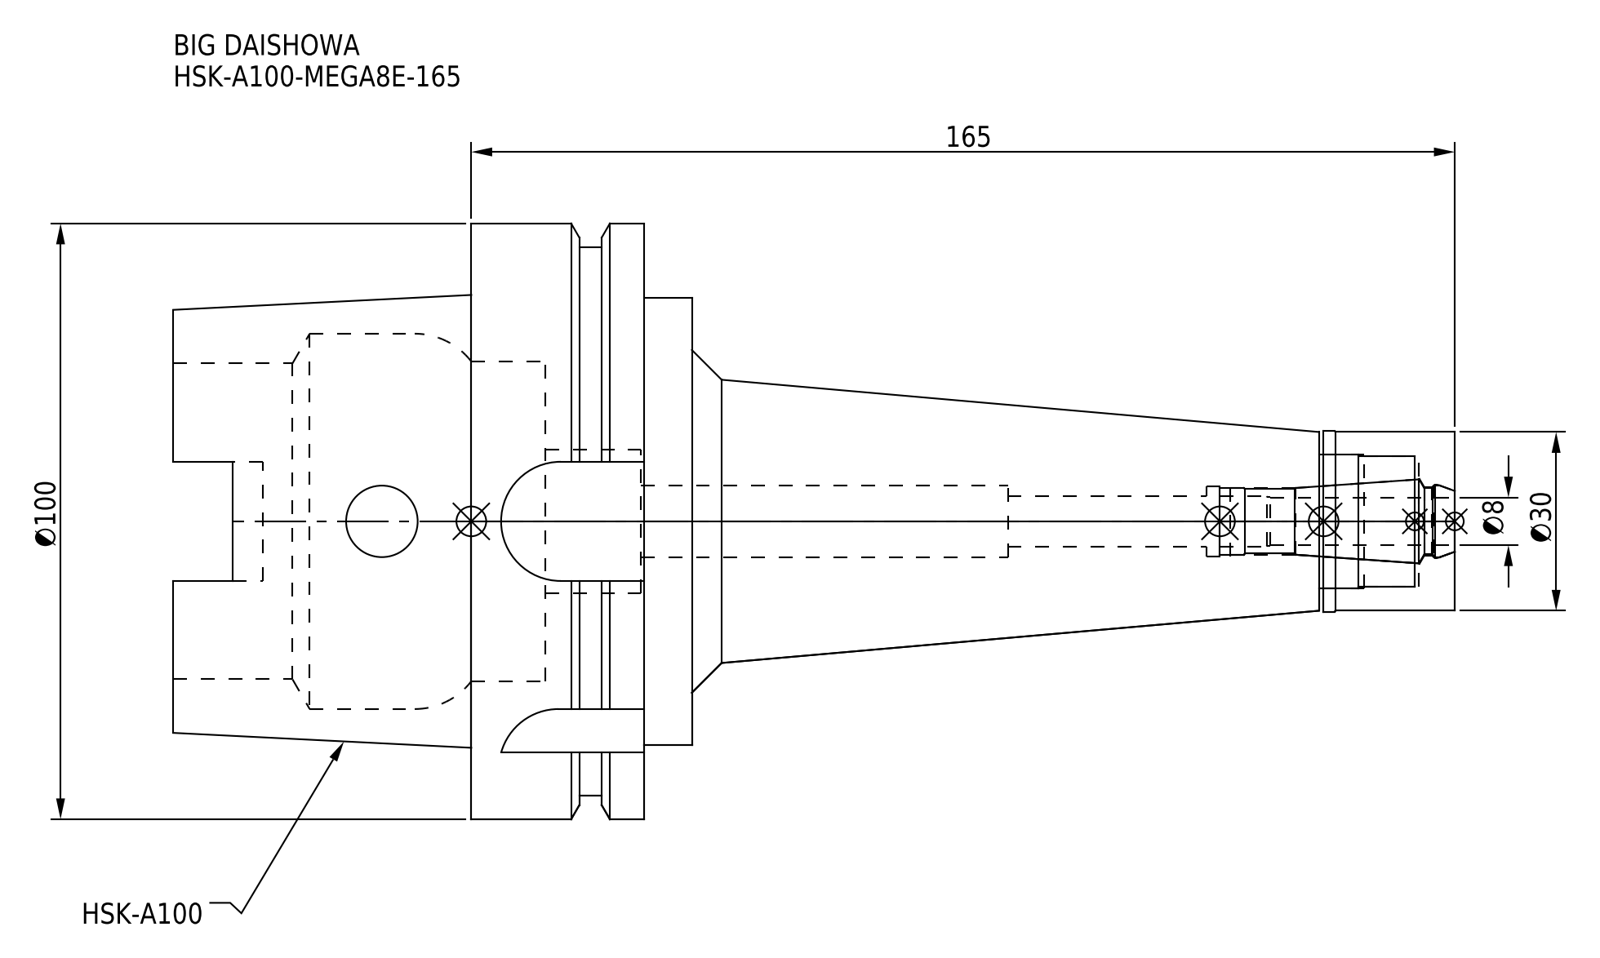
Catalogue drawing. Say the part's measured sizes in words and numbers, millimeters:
The part is named "HSK-A100-MEGA8E-165; MEN8_1.stp; HSK-A100-MEGA8E-165_1.stp; HSK-A100-MEGA8E-165-080-FreeParts (+3 more)". Its 3-D file was written by "SolidWorks 2019 (CONFIG_CONTROL_DESIGN)". It is 2 solids with 126 faces: 42 planar, 56 cylindrical and 28 other. Overall it measures 215 by 100 by 100 millimeters. Its volume is 422 249 cubic millimeters and its surface area 73 563 square millimeters. Round holes: 2 of diameter 12, 1 of diameter 8.4, 1 of diameter 11.2, 1 of diameter 11.4, 1 of diameter 11.8, 1 of diameter 12.3, 1 of diameter 22, 1 of diameter 22.5, 1 of diameter 24, 1 of diameter 53, 1 of diameter 53.8, 1 of diameter 63. Round bosses or shafts: 1 of diameter 100, 1 of diameter 92, 1 of diameter 75, 1 of diameter 30.3, 1 of diameter 30. Partial cylindrical surfaces (rounded edges, fillets, slot ends): 4 of radius 4.88, 4 of radius 10. The main face-to-face distances are 29, 16.55, 12.45, 8, 24.55, 37, 87, 79, 62.45, 50.
